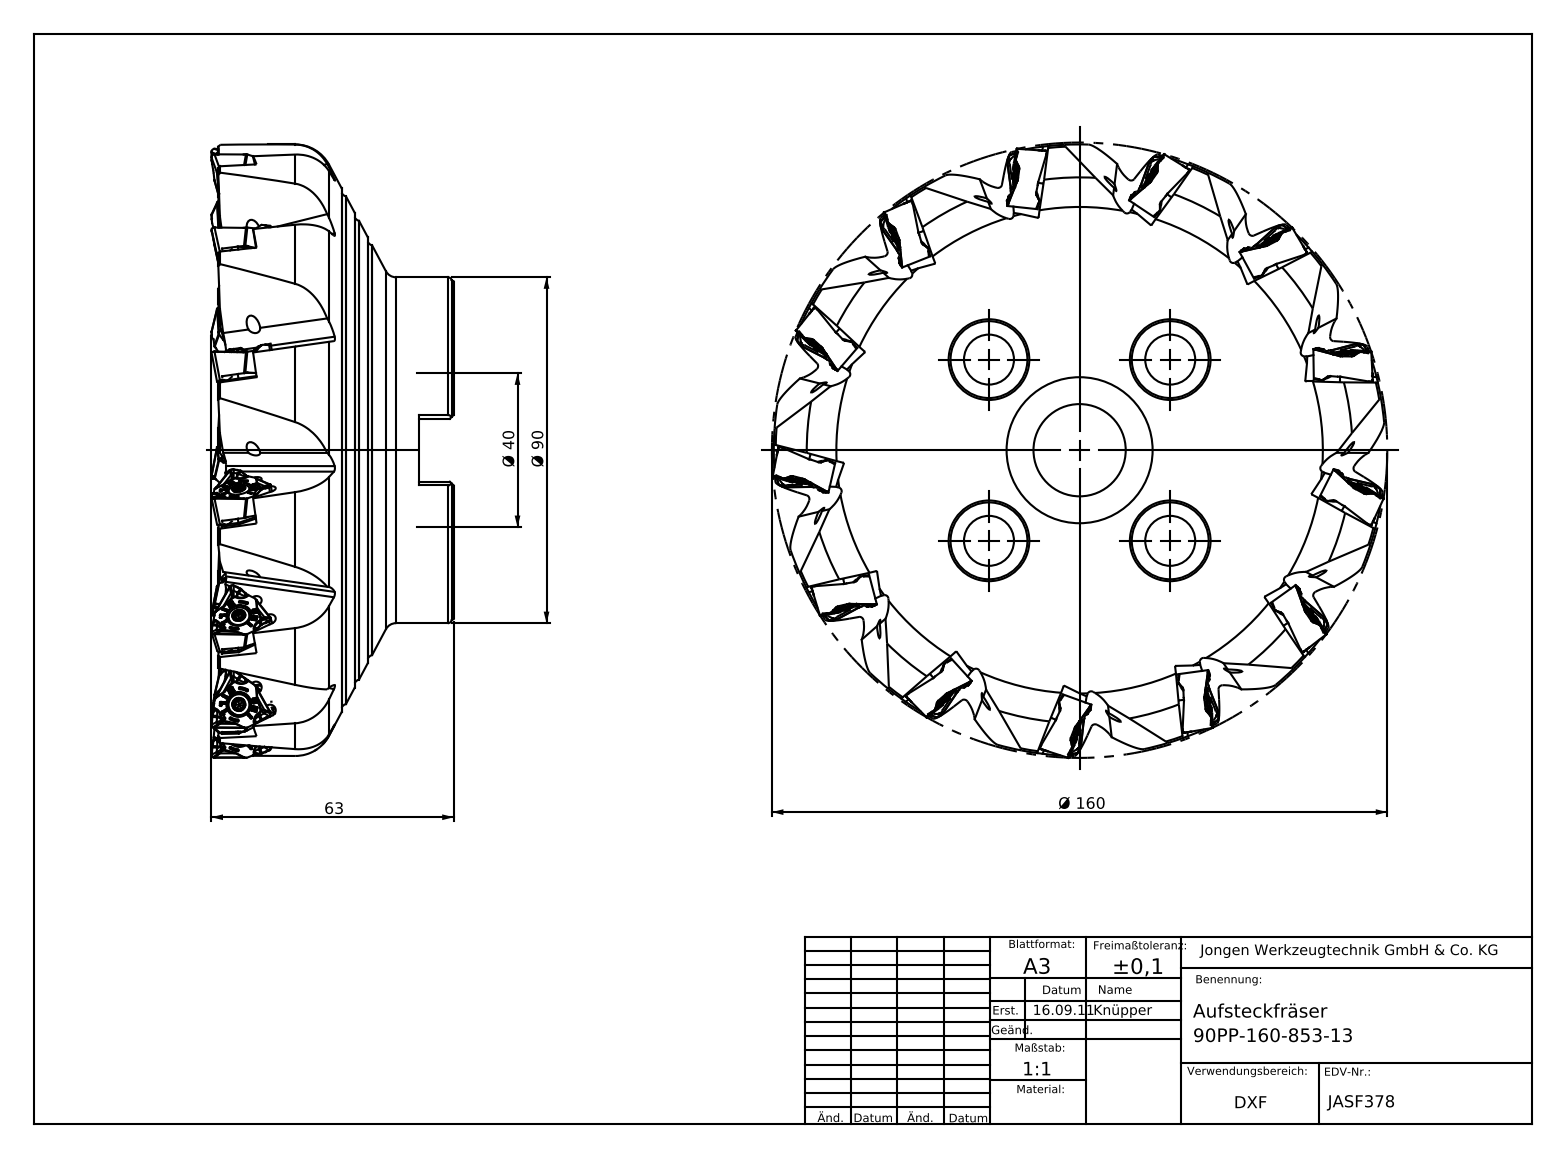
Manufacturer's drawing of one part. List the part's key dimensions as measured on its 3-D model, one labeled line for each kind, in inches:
Part name (STEP PRODUCT): 90PP-160-853-13
STEP written by: SolidWorks 2010 (AUTOMOTIVE_DESIGN)
Units: inches
Bodies: 1 solid, 601 faces (209 planar, 226 cylindrical, 166 other)
Overall size (bounding box): 6.299 × 6.299 × 2.48
Volume: 42.21 in³ · Surface area: 136.5 in²
Round holes (diameter × count): ⌀0.512 ×4, ⌀0.787 ×4, ⌀0.945 ×1, ⌀1.575 ×1, ⌀1.581 ×1, ⌀1.587 ×1
Round bosses / shafts (diameter × count): ⌀6.299 ×1, ⌀6.266 ×1, ⌀3.543 ×1
Partial cylindrical surfaces — rounded edges, fillets, slot ends (radius × count): R0.012 ×91, R0.059 ×26, R0.065 ×13
Main face-to-face distances: 0.077, 2.333, 2.409, 1.975, 0.357, 0.434, 0.354, 1.621, 1.978, 2.055
Hole centre spacings: 1.313, 1.857, 2.626
